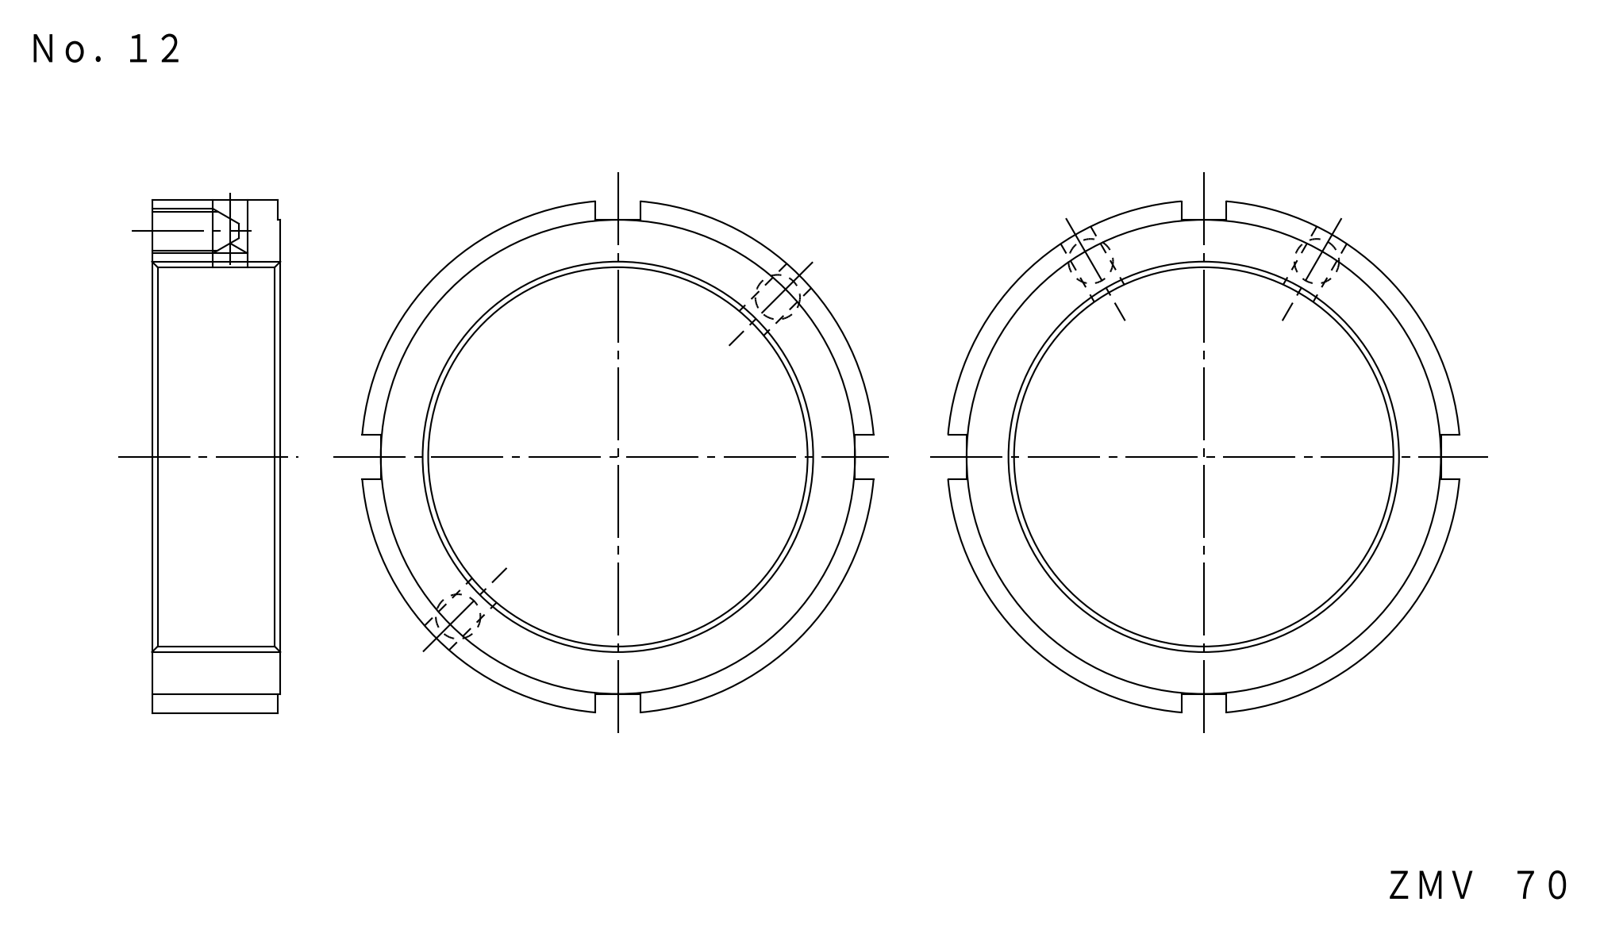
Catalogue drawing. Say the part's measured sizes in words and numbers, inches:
The part is named "FKD ZMV70". Its 3-D file was written by "Autodesk Inventor LT (CONFIG_CONTROL_DESIGN)". It is 1 solid with 32 faces: 18 planar, 10 cylindrical and 4 other. Overall it measures 3.608 by 3.608 by 0.906 inches. Its volume is 3.659 cubic inches and its surface area 28.41 square inches. Round holes: 2 of diameter 0.244, 2 of diameter 0.262, 1 of diameter 2.756. Round bosses or shafts: 1 of diameter 3.622, 1 of diameter 3.346. The main face-to-face distances are 0.906, 0.02, 0.886, 1.516, 1.831, 3.346, 0.315. The hole center spacings are 1.594, 3.189.
